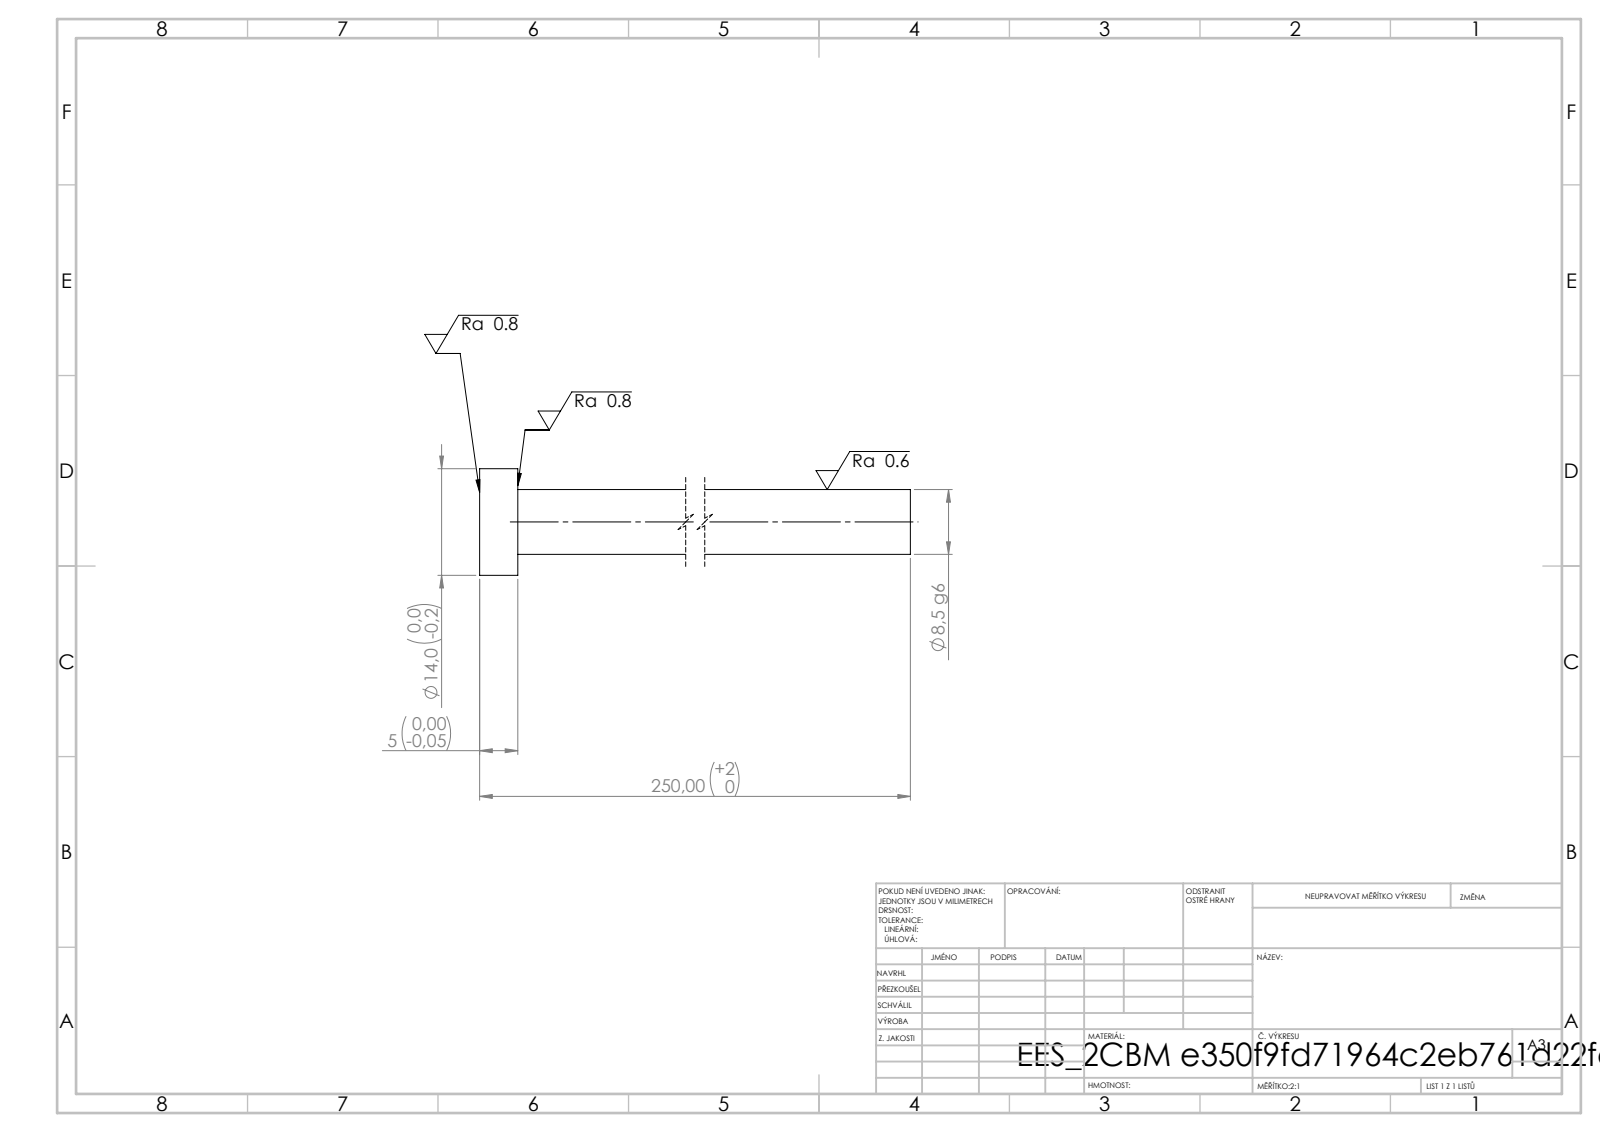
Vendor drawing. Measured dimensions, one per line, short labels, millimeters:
written by: SolidWorks 2019 (CONFIG_CONTROL_DESIGN)
unit: mm
bodies: 1 solid, 7 faces (3 planar, 4 cylindrical, 0 other)
size: 250 × 14 × 14
volume: 14 672 mm³; area: 7 070 mm²
bosses: 1× ⌀14, 1× ⌀8.5
face distances: 5, 250, 245
